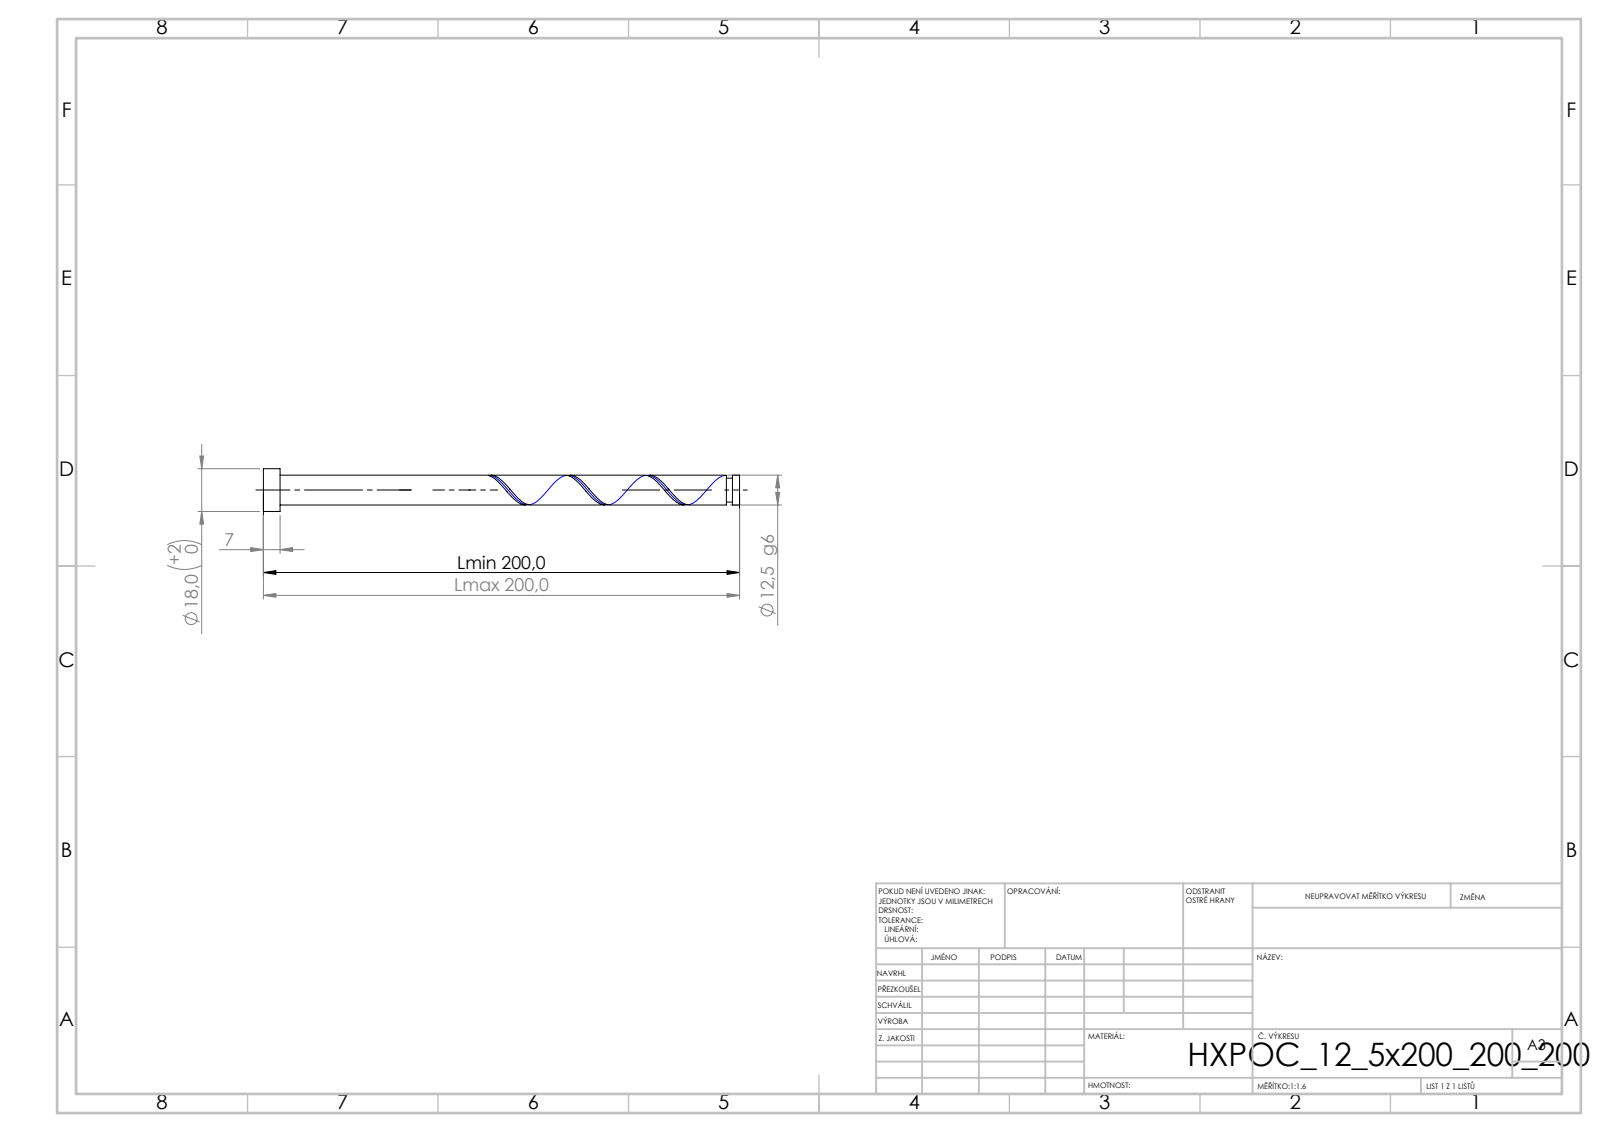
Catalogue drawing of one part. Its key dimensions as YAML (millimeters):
step_written_by: "SolidWorks 2019 (CONFIG_CONTROL_DESIGN)"
units: millimeters
bodies: {solids: 1, faces: 21, planar: 6, cylindrical: 14, other: 1}
overall_size: [200, 18, 18]
volume: 25120
surface_area: 8769
round_bosses_or_shafts:
  - {diameter: 18, count: 1}
  - {diameter: 12.5, count: 1}
  - {diameter: 10, count: 1}
face_to_face_distances: [7, 200, 193, 196.98, 189.98, 3.02, 194.48, 187.48, 2.5, 5.52]
